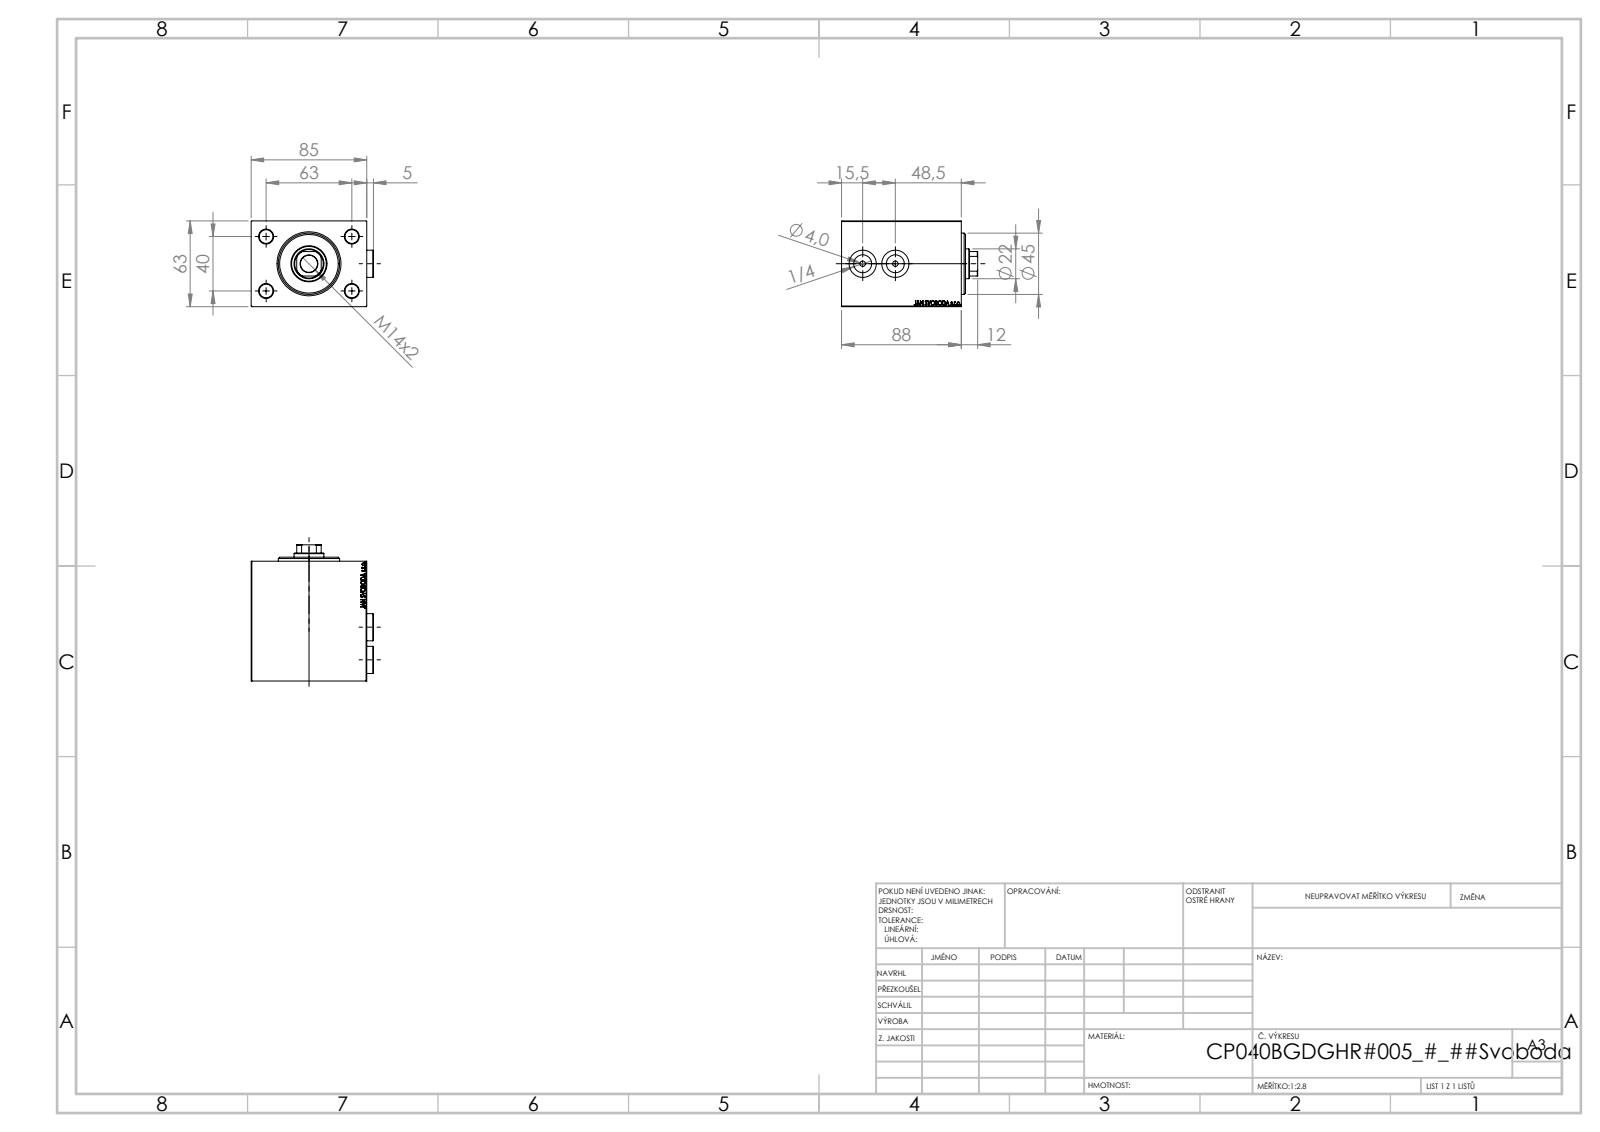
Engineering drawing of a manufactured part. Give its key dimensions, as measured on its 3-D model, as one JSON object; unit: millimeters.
{"part_name": "V450CP_B; V450CP_B_VCP; PLUG; V450CP_VC_B", "step_written_by": "SolidWorks 2019 (CONFIG_CONTROL_DESIGN)", "units": "millimeters", "bodies": {"solids": 5, "faces": 955, "planar": 439, "cylindrical": 82, "other": 434}, "overall_size": [100, 89.9, 63], "volume_mm3": 452168, "surface_area_mm2": 79014, "round_holes": [[4, 4], [10, 4], [9.73, 2], [13.16, 2], [15, 2], [20, 2], [12.5, 1], [22, 1], [25.5, 1], [26.5, 1], [40, 1], [42, 1]], "partial_cylinders_radius": [[10.5, 1]], "face_to_face_distances": [63, 85, 88, 12, 76, 5, 41, 84.9, 47, 35], "hole_center_spacings": [37.31, 40, 63, 74.63, 24, 39.18]}
